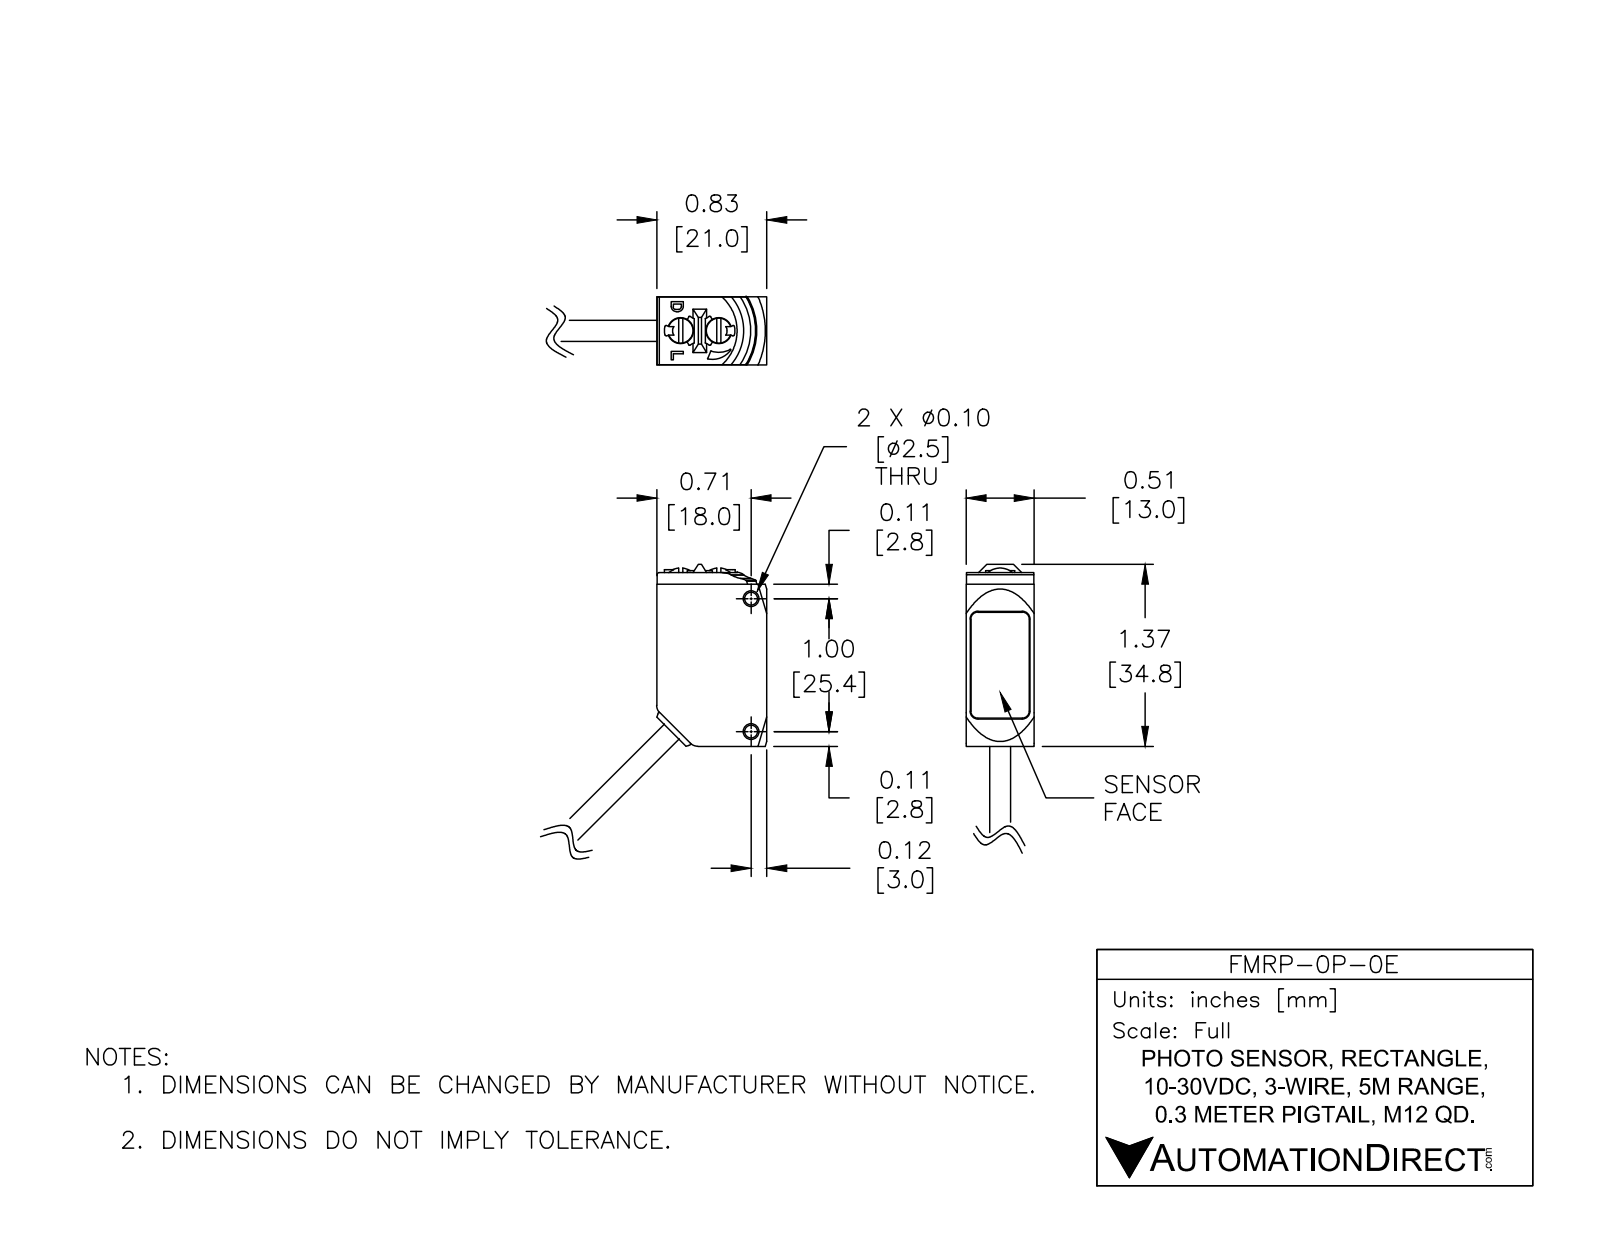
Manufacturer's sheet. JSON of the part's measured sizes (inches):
{"part_name": "FMRP-0P-0E", "step_written_by": "SolidWorks 2017 (AUTOMOTIVE_DESIGN)", "units": "inches", "bodies": {"solids": 1, "faces": 186, "planar": 89, "cylindrical": 72, "other": 25}, "overall_size": [2.084, 1.541, 0.512], "volume_in3": 0.542, "surface_area_in2": 5.476, "round_holes": [[0.097, 2], [0.197, 2]], "round_bosses_or_shafts": [[0.189, 2], [0.157, 1]], "partial_cylinders_radius": [[0.018, 7], [0.02, 7], [0.008, 4], [0.01, 4], [0.051, 4], [0.059, 4], [0.004, 3], [0.018, 2]], "face_to_face_distances": [0.512, 0.827, 1.307, 0.035, 0.51, 0.031, 0.48, 0.037, 0.474, 0.472], "hole_center_spacings": [0.287, 1]}
